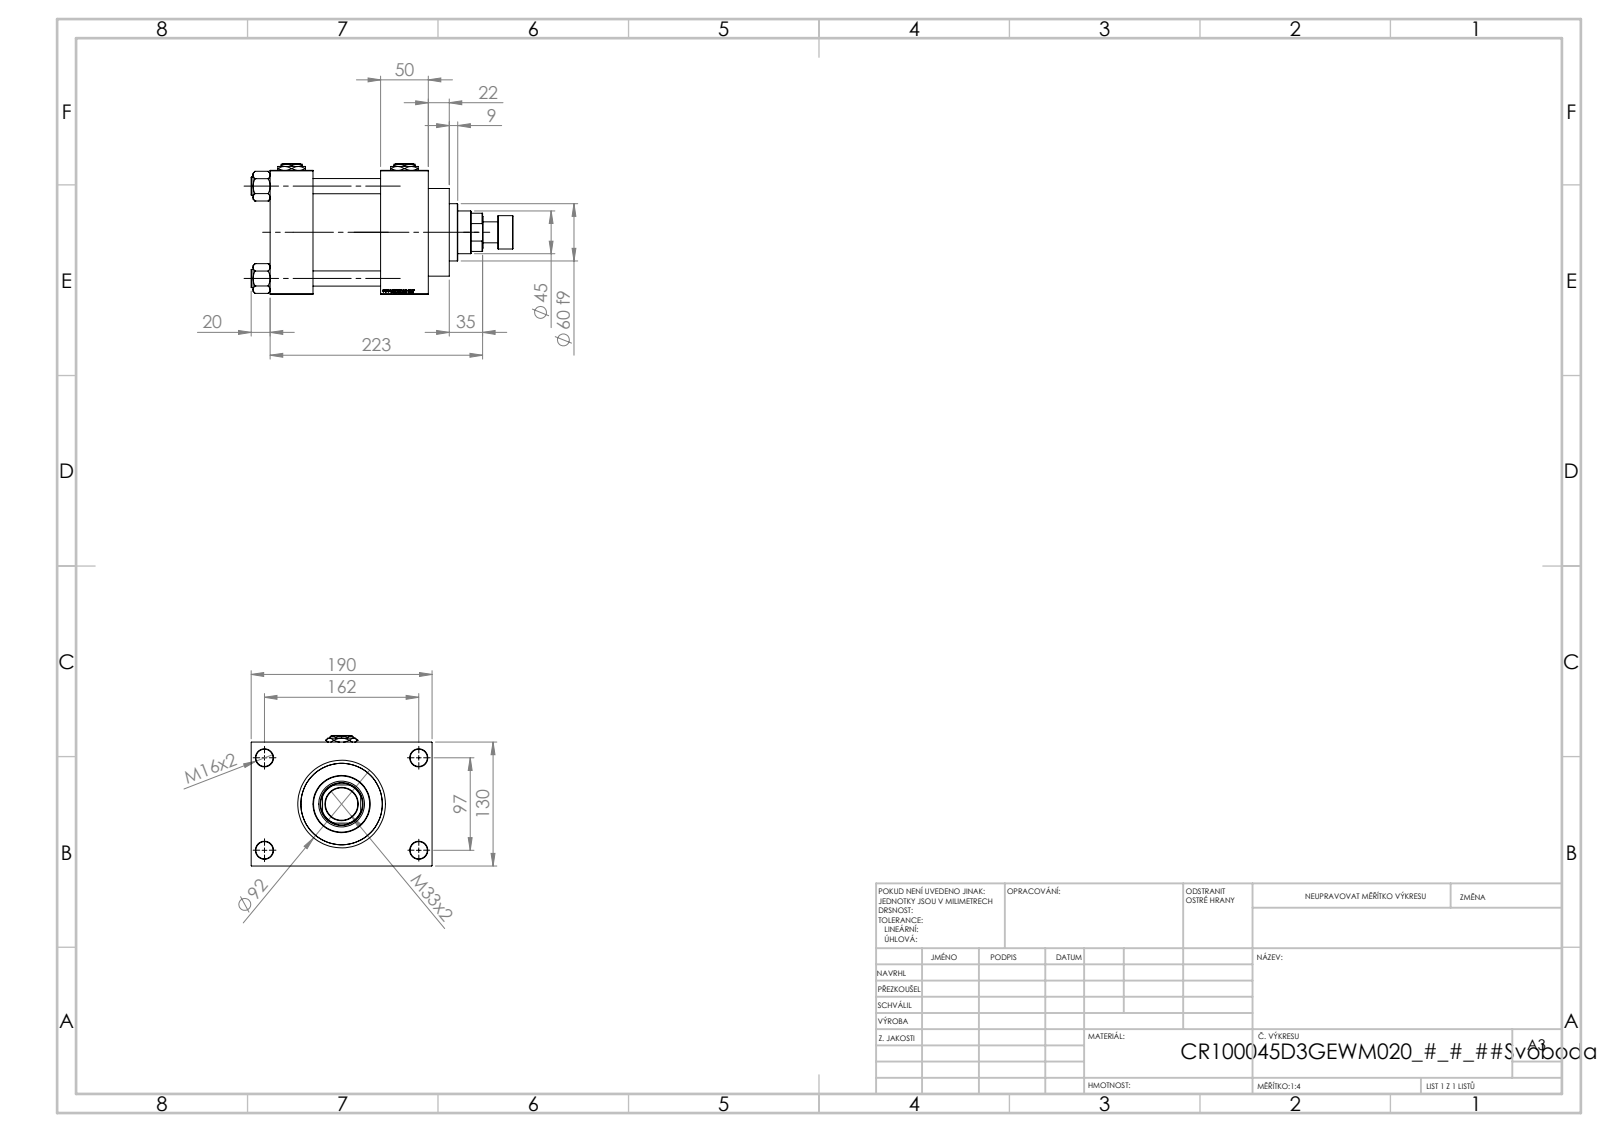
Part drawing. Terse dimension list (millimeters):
name: V215CR_D_Body; NUT_M5_D; V215CR_VCP_D; V215CR_ROD_END_W (+3 more)
written by: SolidWorks 2019 (CONFIG_CONTROL_DESIGN)
unit: mm
bodies: 14 solids, 1267 faces (597 planar, 104 cylindrical, 566 other)
size: 275 × 190 × 137
volume: 2 614 000 mm³; area: 365 097 mm²
holes: 4× ⌀16, 4× ⌀18, 2× ⌀7, 2× ⌀26.44, 2× ⌀35, 1× ⌀31.5, 1× ⌀45, 1× ⌀48, 1× ⌀76, 1× ⌀85.5, 1× ⌀100
bosses: 4× ⌀19, 1× ⌀106, 1× ⌀92, 1× ⌀60, 1× ⌀35, 1× ⌀22
rounds: 1× R22
face distances: 130, 45, 116, 71, 166, 121, 50, 160, 30, 20
hole spacings: 32.55, 68.52, 94.41, 96.9, 102.27, 129.45, 161.73, 97
